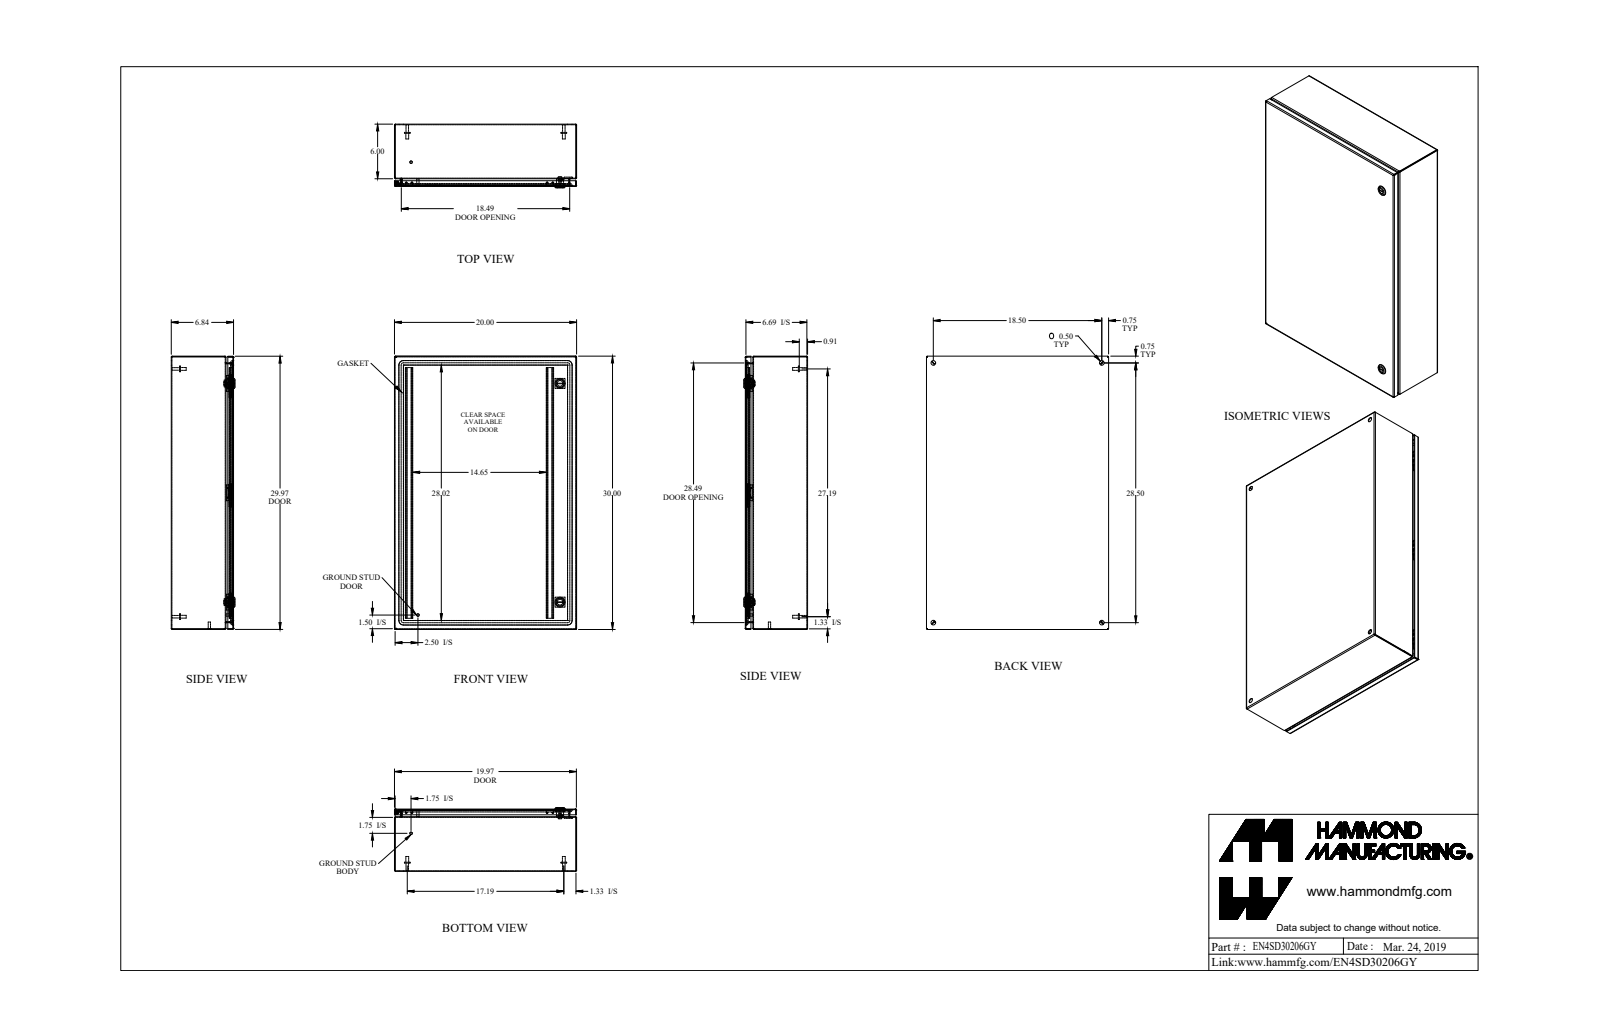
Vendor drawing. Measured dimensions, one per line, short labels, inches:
name: EN4SD30206GY_Default
written by: SolidWorks 2019 (CONFIG_CONTROL_DESIGN)
unit: in
bodies: 31 solids, 885 faces (422 planar, 295 cylindrical, 168 other)
size: 30 × 20 × 6.997
volume: 157.4 in³; area: 4 430 in²
holes: 4× ⌀0.5, 2× ⌀0.232, 2× ⌀0.625, 2× ⌀0.785, 1× ⌀0.172, 1× ⌀0.24, 1× ⌀0.242
bosses: 4× ⌀0.625, 4× ⌀0.313, 4× ⌀0.27, 2× ⌀1.1, 2× ⌀0.525, 2× ⌀0.281, 2× ⌀0.25, 1× ⌀0.455
rounds: 20× R0.036, 20× R0.108, 12× R0.043, 12× R0.081, 12× R0.382, 8× R19.003, 6× R0.006, 6× R0.062
face distances: 0.072, 6.765, 6.693, 6.837, 19.928, 29.928, 19.856, 20, 0.837, 5.928
hole spacings: 18.5, 28.5, 33.978, 2.493, 2.494, 17.572, 17.572, 23.999
